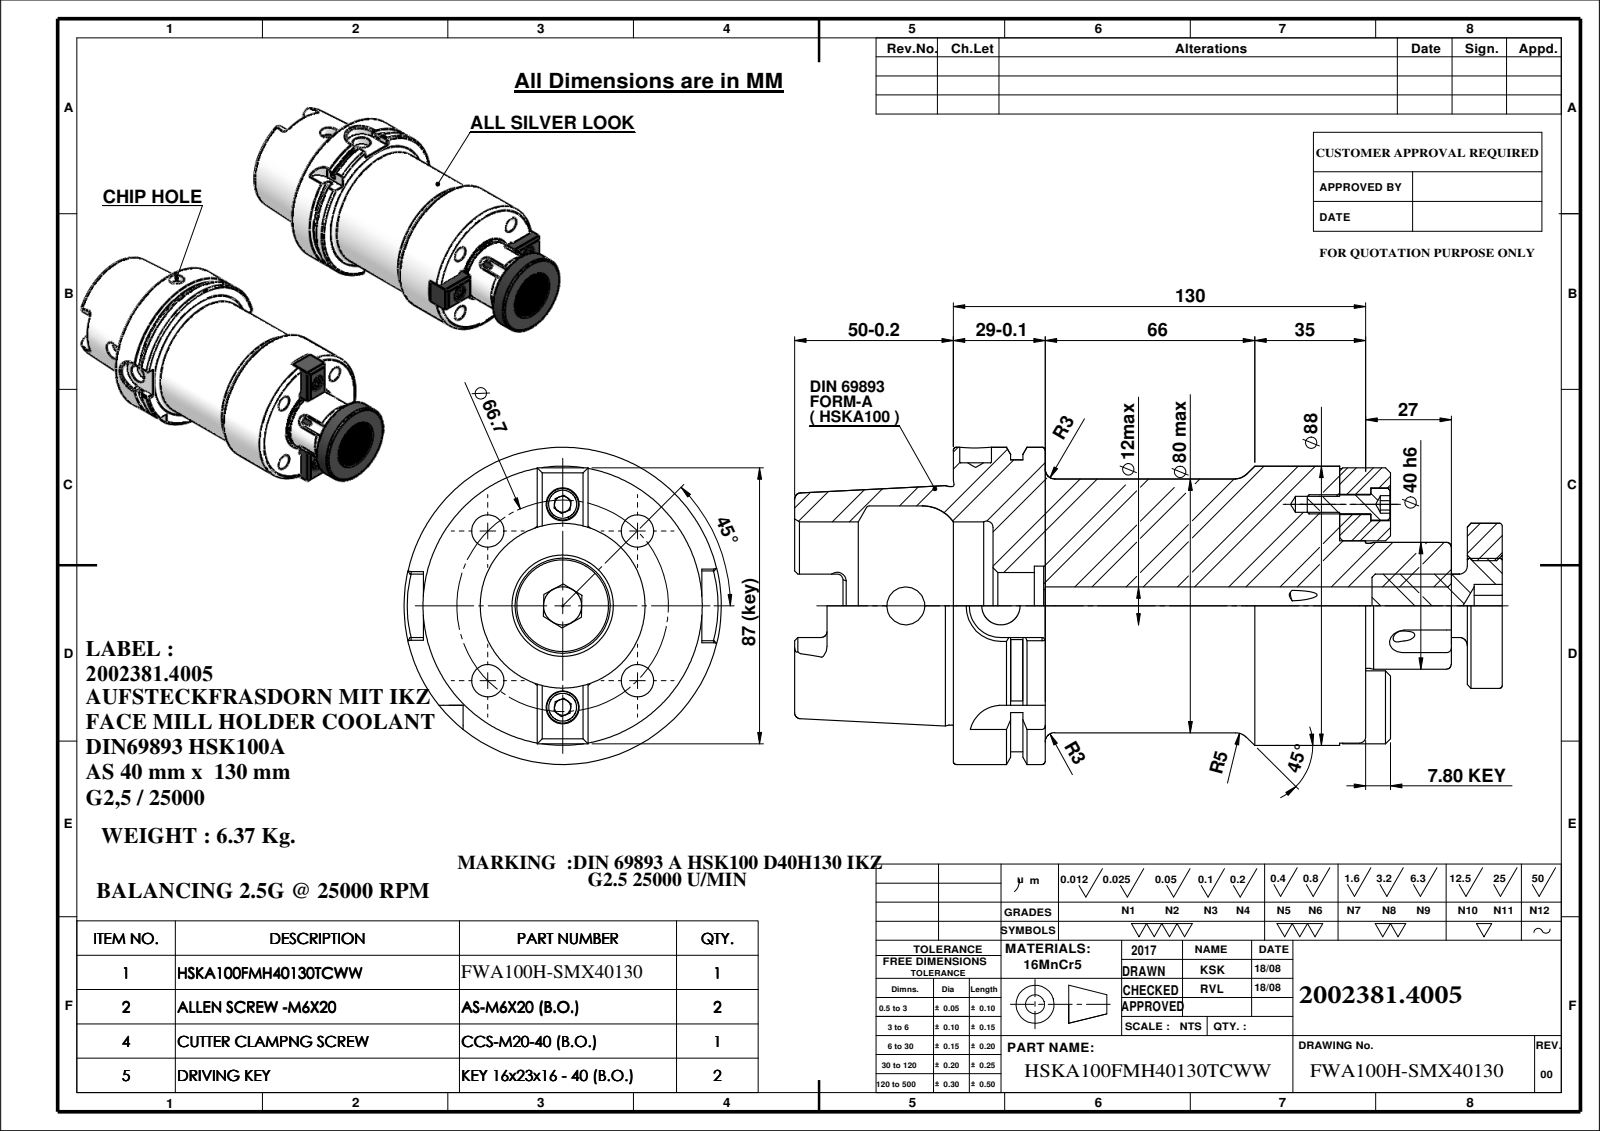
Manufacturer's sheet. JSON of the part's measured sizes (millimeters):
{"part_name": "CCS-M20-40; Part1^HSKA100 SMS40 100 TC WW; 91100A-AS540130; HSKA100FMH40130TCWW (+4 more)", "step_written_by": "SolidWorks 2009 (CONFIG_CONTROL_DESIGN)", "units": "millimeters", "bodies": {"solids": 7, "faces": 408, "planar": 148, "cylindrical": 112, "other": 148}, "overall_size": [223, 100, 100], "volume_mm3": 841761, "surface_area_mm2": 108575, "round_holes": [[10.2, 5], [4, 4], [12, 3], [5, 2], [6.4, 2], [10.4, 2], [10, 1], [21, 1], [25, 1], [28.5, 1], [53, 1], [63, 1]], "round_bosses_or_shafts": [[10, 2], [6, 2], [100, 1], [92, 1], [88, 1], [80, 1], [75.16, 1], [52, 1]], "partial_cylinders_radius": [[1.8, 6], [3, 4], [4, 4], [4.88, 4], [10, 2], [11, 1]], "face_to_face_distances": [130, 16, 173, 43, 109.3, 29, 101, 144, 12.5, 16.5], "hole_center_spacings": [25.04, 33.35, 47.16, 60.38, 32, 66.69, 30, 64]}
